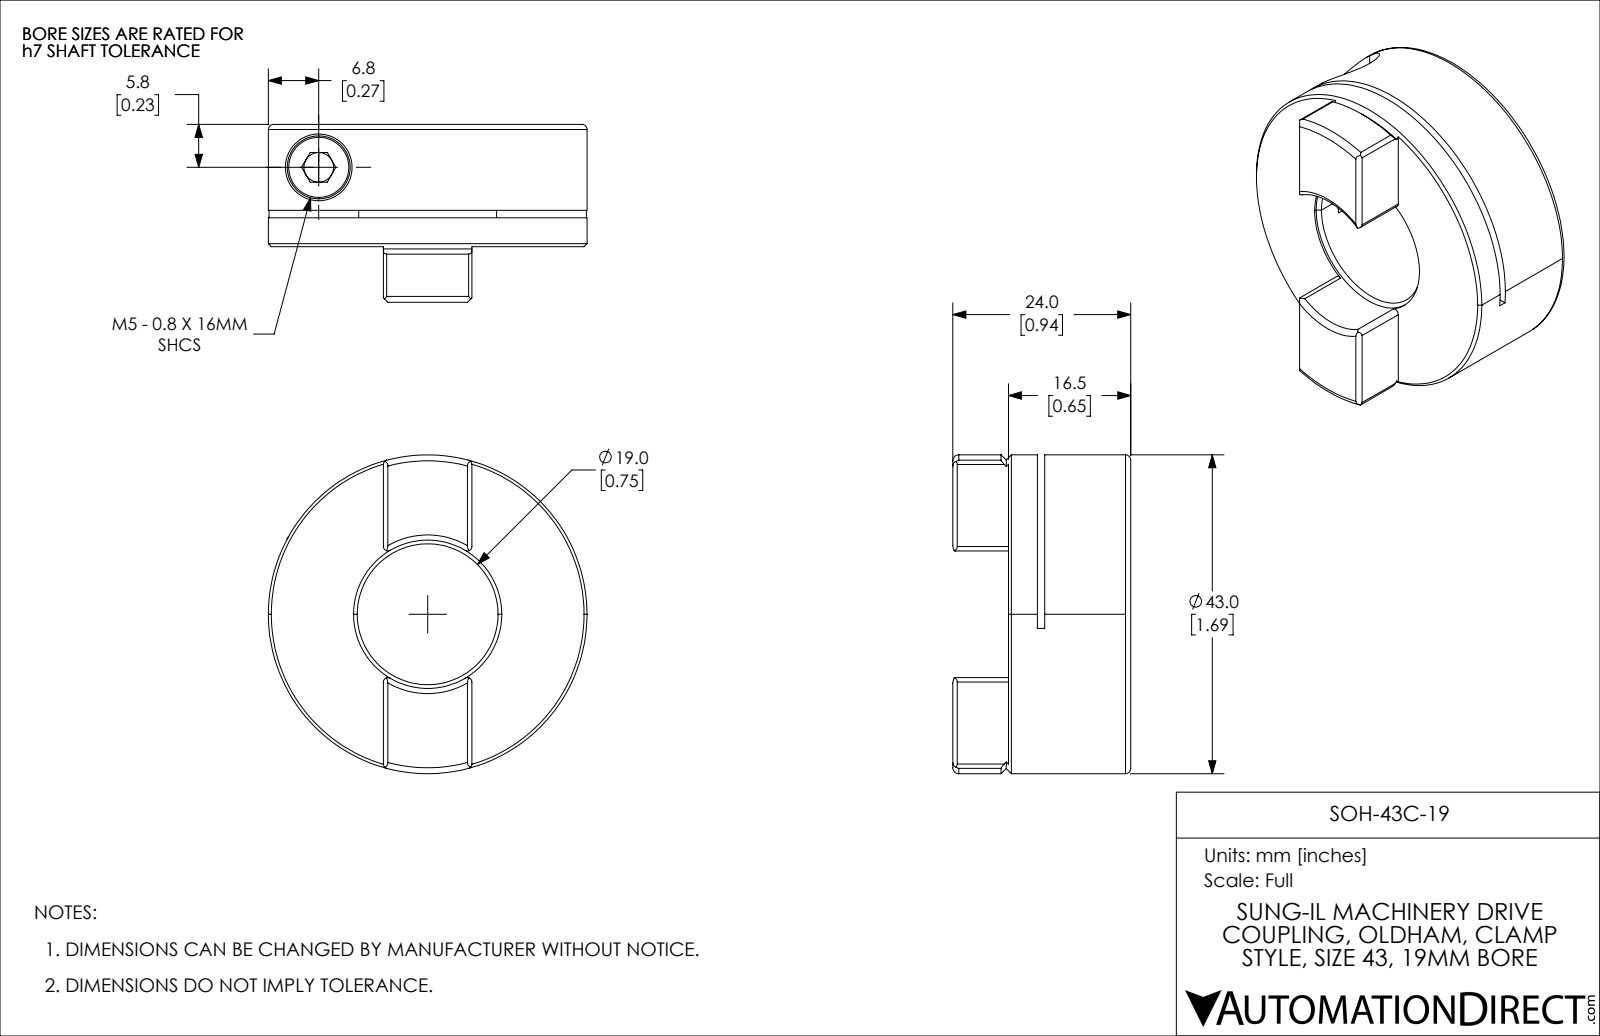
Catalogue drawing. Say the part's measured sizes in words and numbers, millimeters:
The part is named "SOH-43C-19". Its 3-D file was written by "SolidWorks 2021 (CONFIG_CONTROL_DESIGN)". It is 2 solids with 94 faces: 38 planar, 33 cylindrical and 23 other. Overall it measures 43 by 43 by 24 millimeters. Its volume is 20 081 cubic millimeters and its surface area 8 589 square millimeters. Round holes: 1 of diameter 4, 1 of diameter 4.2, 1 of diameter 5.4, 1 of diameter 9, 1 of diameter 19, 1 of diameter 20. Round bosses or shafts: 1 of diameter 43, 1 of diameter 8.5, 1 of diameter 5. Partial cylindrical surfaces (rounded edges, fillets, slot ends): 8 of radius 0.6, 1 of radius 37.5. The main face-to-face distances are 16.5, 12.6, 3.9, 11.6, 1, 4.9, 24, 12.4, 11.4, 7.5.
